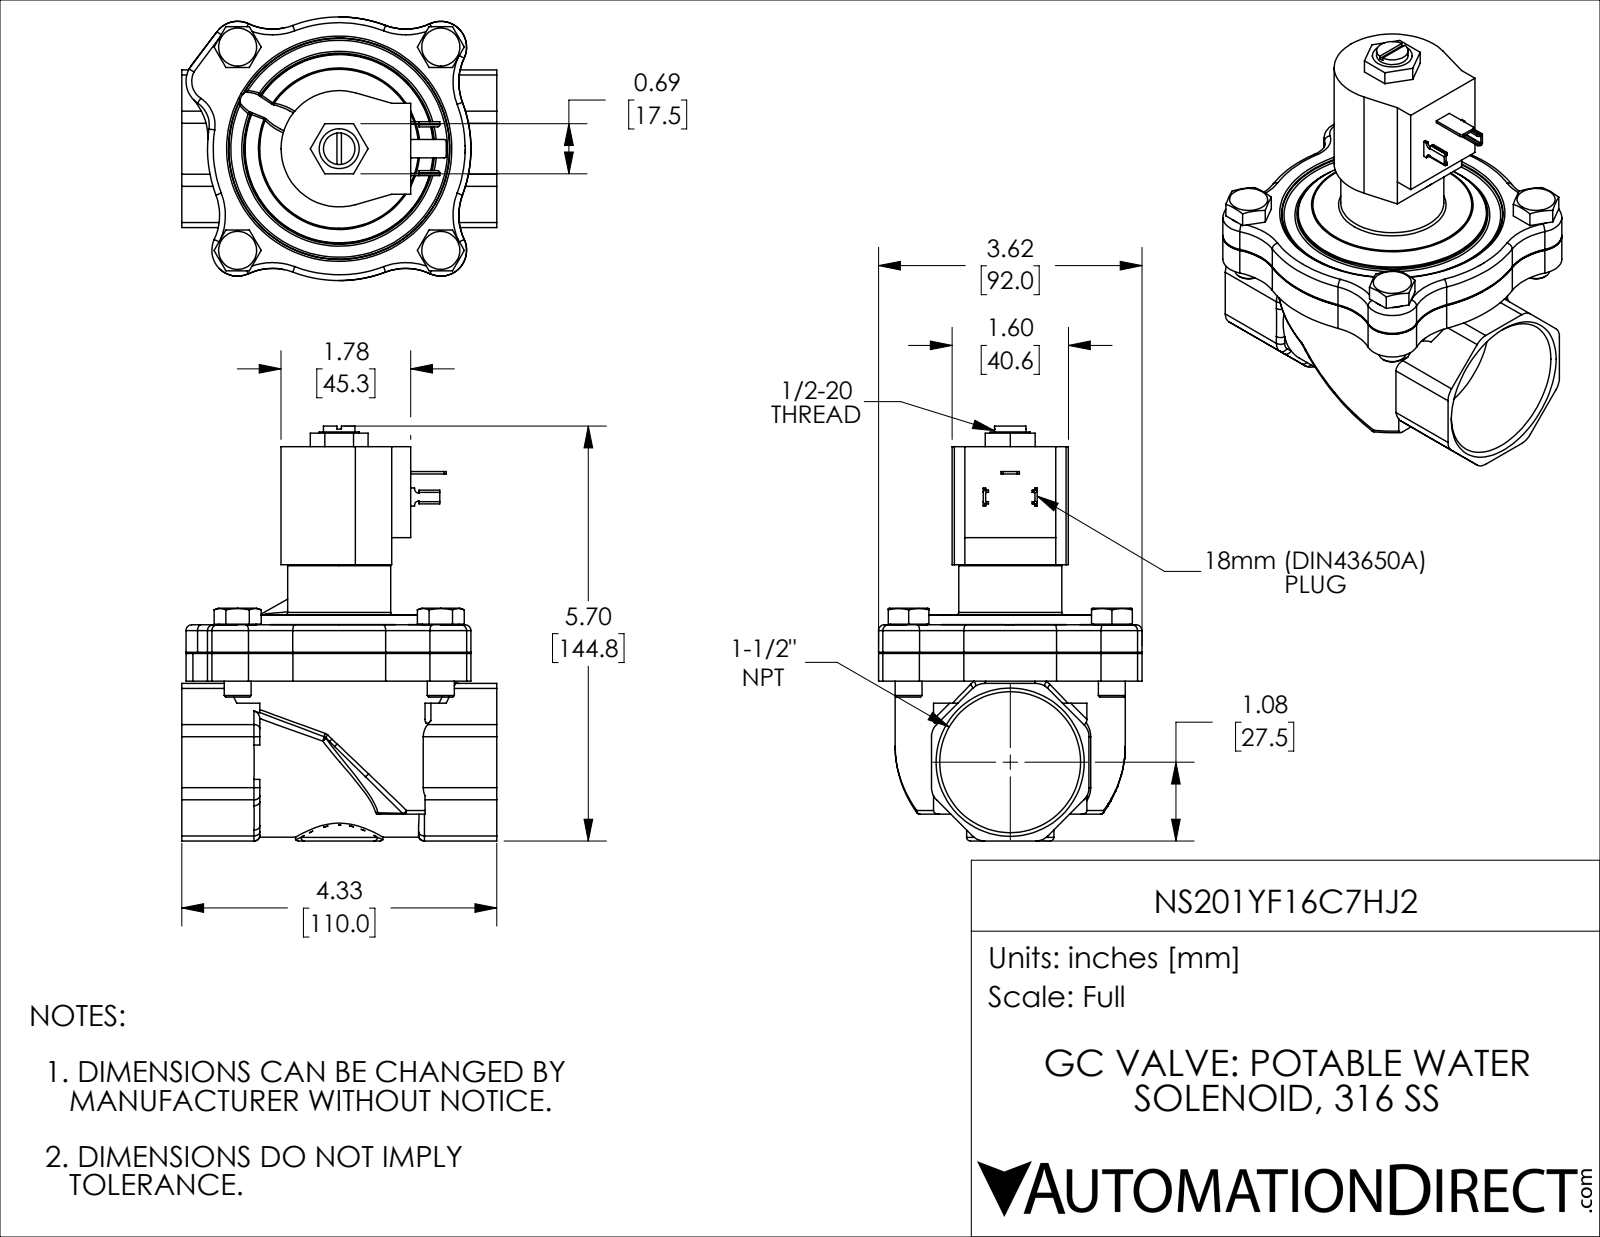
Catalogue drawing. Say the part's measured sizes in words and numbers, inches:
The part is named "NS201YF16C7HJ2". Its 3-D file was written by "SolidWorks 2018 (AUTOMOTIVE_DESIGN)". It is 12 solids with 541 faces: 170 planar, 156 cylindrical and 215 other. Overall it measures 5.701 by 4.33 by 3.622 inches. Its volume is 26.21 cubic inches and its surface area 138.4 square inches. Round holes: 4 of diameter 0.375, 4 of diameter 0.433, 1 of diameter 0.125, 1 of diameter 0.488, 1 of diameter 0.846, 1 of diameter 0.949, 1 of diameter 1.937. Round bosses or shafts: 4 of diameter 0.504, 4 of diameter 0.37, 1 of diameter 3.165, 1 of diameter 1.417, 1 of diameter 1.2, 1 of diameter 0.547, 1 of diameter 0.434. Partial cylindrical surfaces (rounded edges, fillets, slot ends): 15 of radius 0.787, 13 of radius 0.08, 8 of radius 0.03, 8 of radius 0.236, 8 of radius 0.354, 2 of radius 0.362, 2 of radius 1.811, 1 of radius 0.031. The main face-to-face distances are 0.382, 0.775, 0.393, 3.222, 2.84, 2.447, 1.83, 1.602, 1.22, 0.827. The hole center spacings are 2.795, 1.976, 1.977, 2.794, 2.795, 3.952, 3.953.
